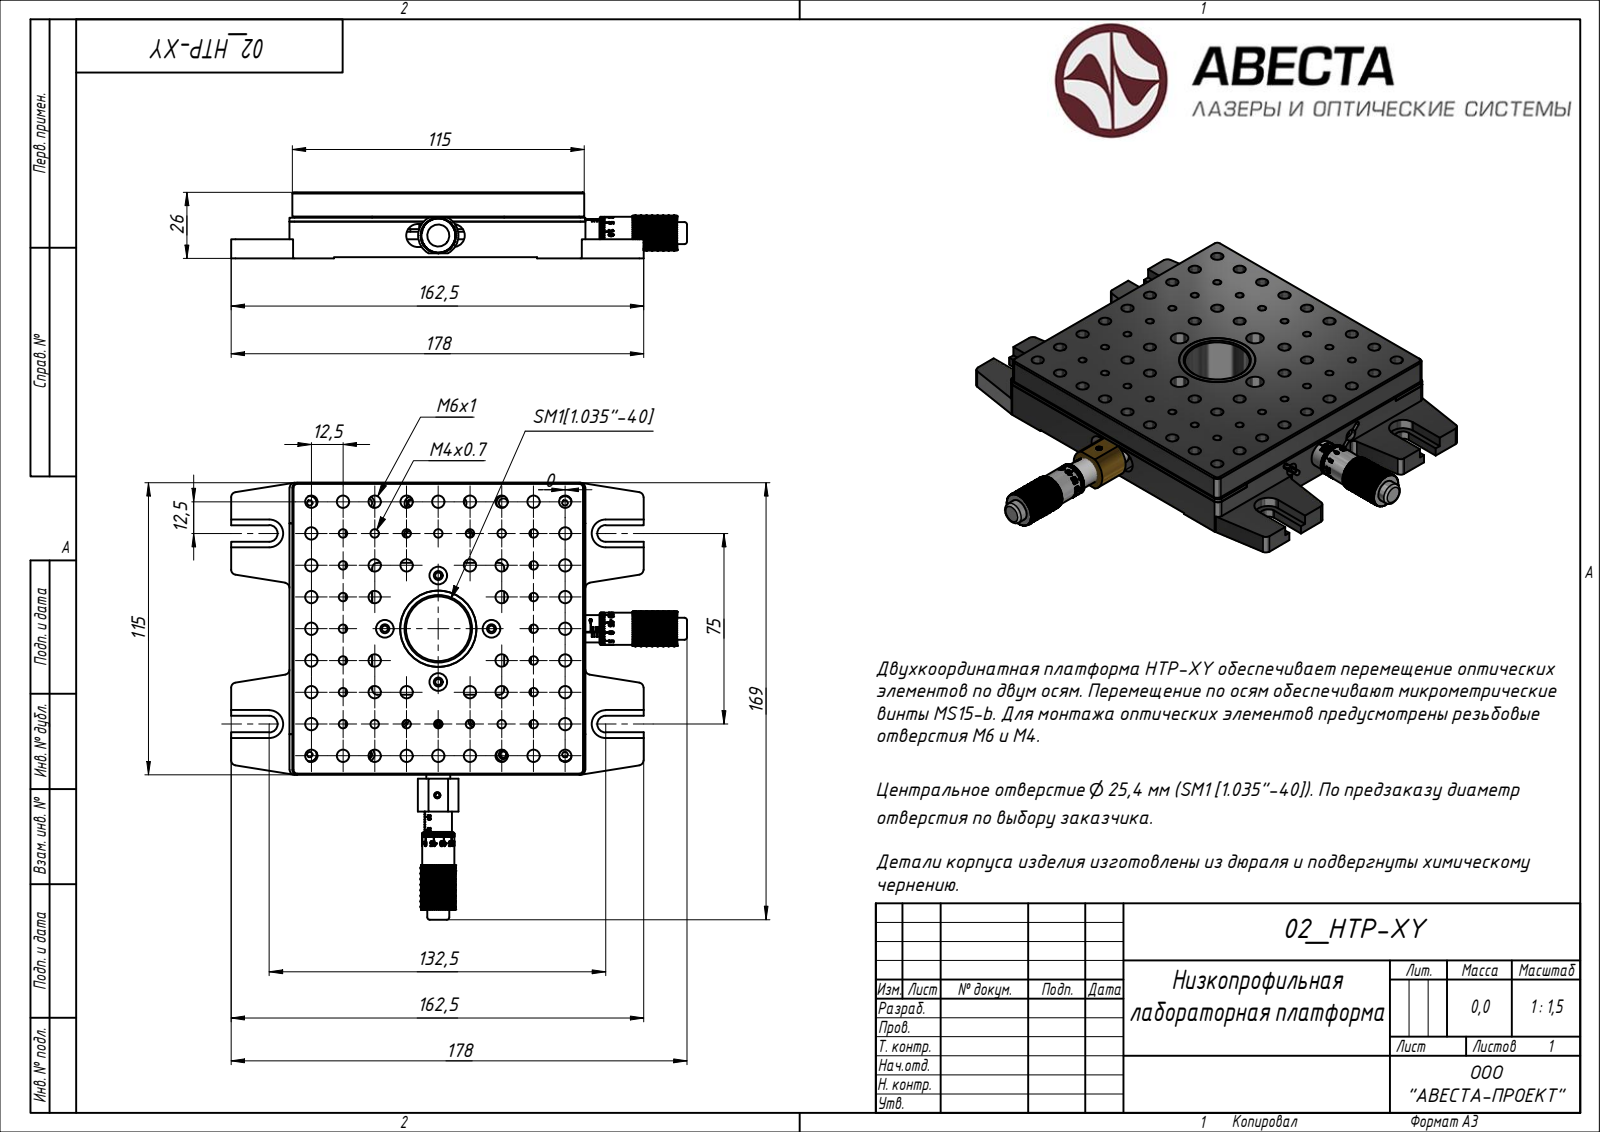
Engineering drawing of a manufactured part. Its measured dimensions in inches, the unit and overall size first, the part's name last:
Units: inches
Overall size (bounding box): 7.07 × 6.772 × 1.024
Round holes (diameter × count): ⌀0.194 ×31, ⌀0.128 ×24, ⌀0.097 ×16, ⌀0.157 ×12, ⌀0.138 ×11, ⌀0.062 ×6, ⌀0.091 ×6, ⌀0.197 ×6, ⌀0.098 ×4, ⌀0.194 ×4, ⌀0.276 ×4, ⌀0.122 ×2
Round bosses / shafts (diameter × count): ⌀0.028 ×6, ⌀0.211 ×4, ⌀0.118 ×4, ⌀0.531 ×2, ⌀0.5 ×2, ⌀0.425 ×2, ⌀0.341 ×2, ⌀0.126 ×2
Partial cylindrical surfaces — rounded edges, fillets, slot ends (radius × count): R0.079 ×54, R0.097 ×9, R0.097 ×9, R0.039 ×8, R0.048 ×6, R0.048 ×6, R0.128 ×4, R0.217 ×4
Main face-to-face distances: 0.02, 0.138, 0.63, 0.492, 0.374, 0.61, 0.394, 0.157, 0.118, 0.65
Hole centre spacings: 0.77, 1.283, 1.535, 0.02, 0.574, 0.984, 1.556, 0.679
Volume: 17.88 in³ · Surface area: 178.8 in²
Bodies: 11 solids, 7229 faces (5838 planar, 815 cylindrical, 576 other)
STEP written by: Rhino 7.34 (AUTOMOTIVE_DESIGN)
